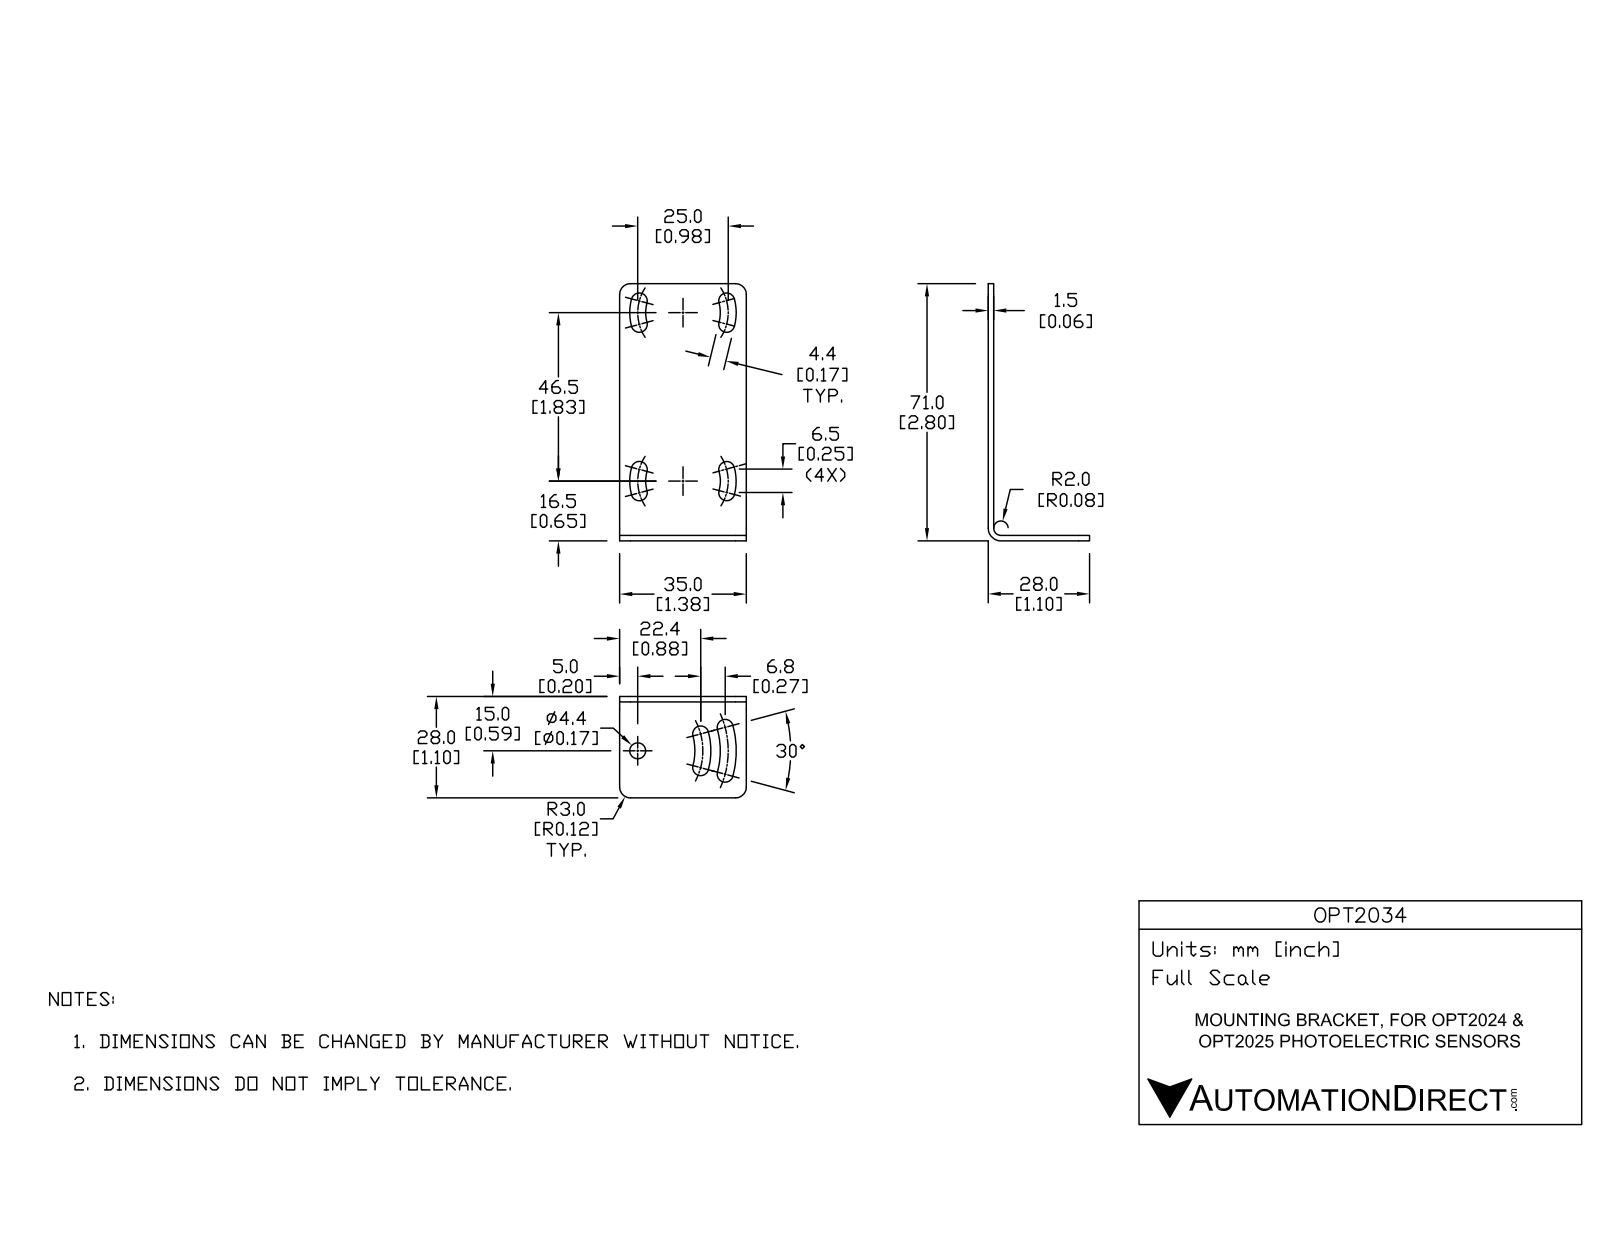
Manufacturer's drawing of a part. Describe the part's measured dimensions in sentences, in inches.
Its 3-D file was written by "Unknown (CONFIG_CONTROL_DESIGN)". It is 1 solid with 39 faces: 8 planar, 31 cylindrical and 0 other. Overall it measures 2.795 by 1.378 by 1.102 inches. Its volume is 0.279 cubic inches and its surface area 10.48 square inches. Round holes: 1 of diameter 0.173. Partial cylindrical surfaces (rounded edges, fillets, slot ends): 10 of radius 0.087, 4 of radius 0.118, 2 of radius 0.086, 2 of radius 0.406, 2 of radius 0.579, 1 of radius 0.079, 1 of radius 0.138, 1 of radius 0.406. The main face-to-face distances are 0.059, 1.378, 1.102, 1.043, 2.736, 2.795.
